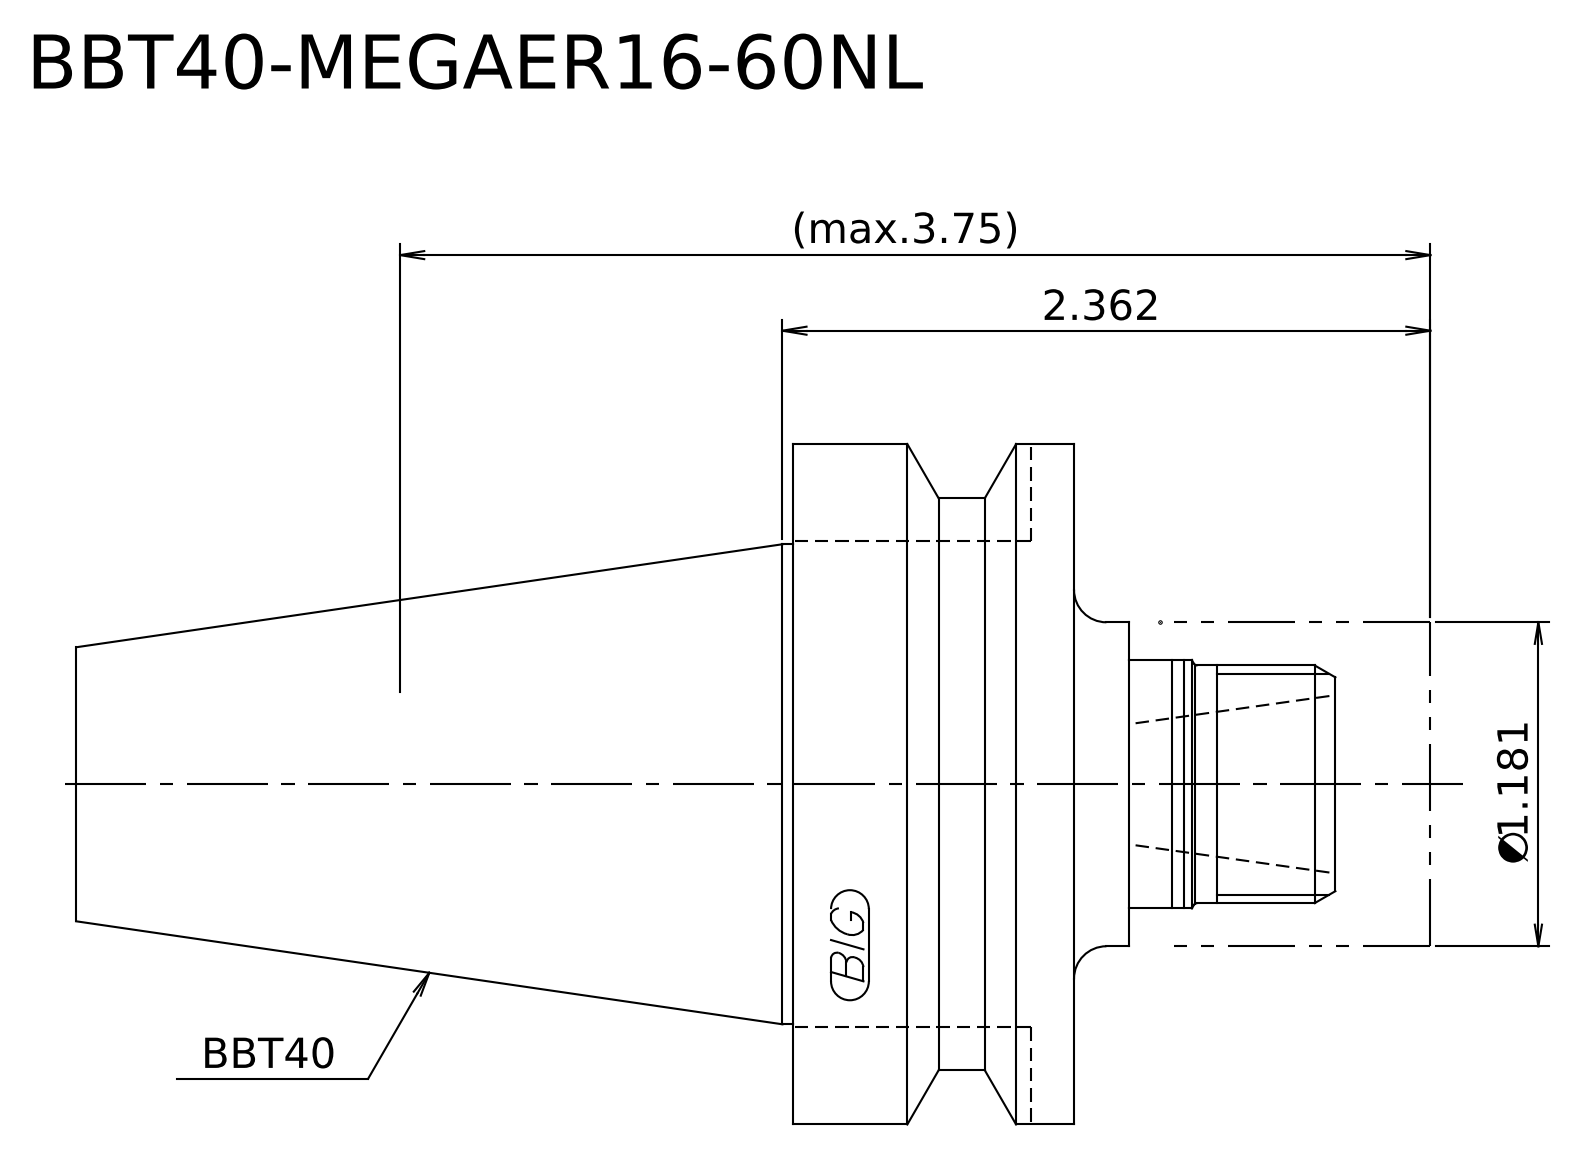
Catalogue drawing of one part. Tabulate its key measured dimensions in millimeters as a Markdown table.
| quantity | value |
| --- | --- |
| STEP written by | Kubotek KeyCreator 2011 V10.0.2 (22737) (automotive_design) |
| units | millimeters |
| bodies | 2 solids, 21 faces (7 planar, 8 cylindrical, 6 other) |
| overall size | 125.4 × 63 × 63 |
| volume | 169 276 mm³ |
| surface area | 23 910 mm² |
| round bosses / shafts (diameter × count) | 63 × 1, 53 × 1, 44.45 × 1, 30 × 1, 23 × 1, 22 × 1 |
| main face-to-face distances | 26, 8, 34, 25, 33, 59, 125.4, 100.4, 92.4, 66.4 |
